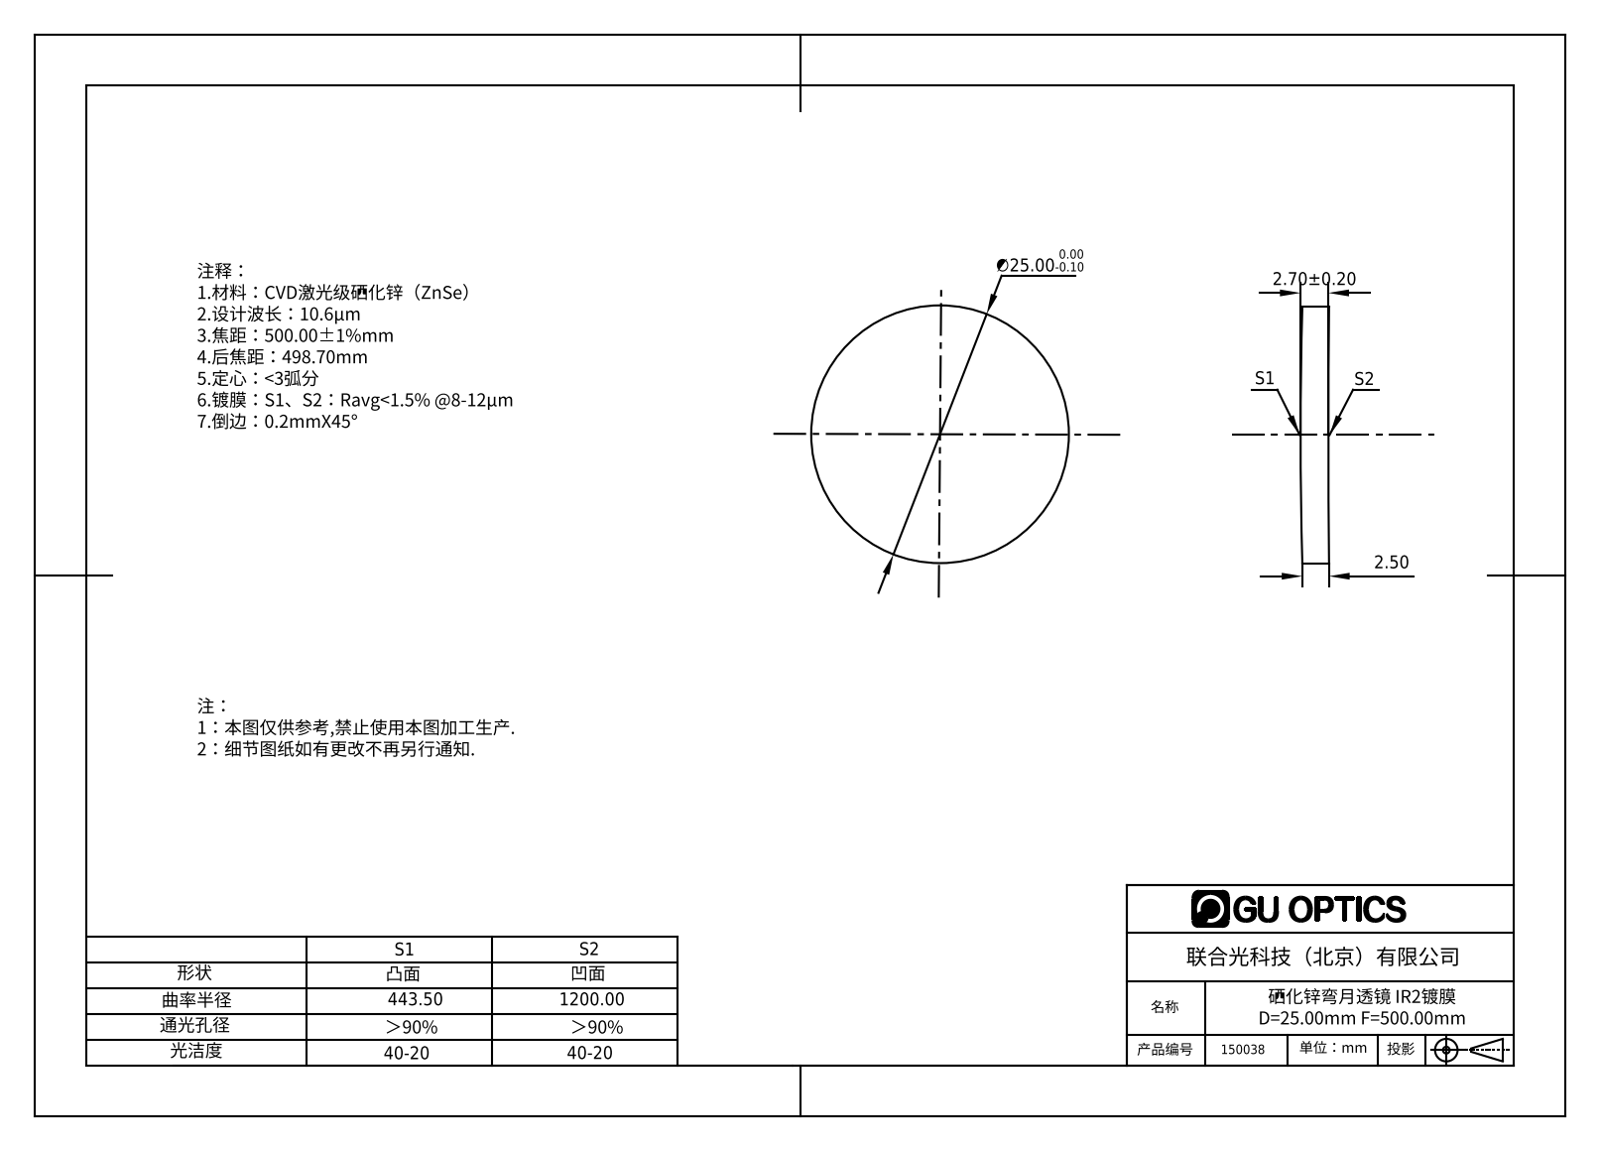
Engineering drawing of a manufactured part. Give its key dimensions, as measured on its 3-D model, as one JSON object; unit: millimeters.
{"part_name": "150013", "step_written_by": "SolidWorks 2016 (AUTOMOTIVE_DESIGN)", "units": "millimeters", "bodies": {"solids": 1, "faces": 6, "planar": 0, "cylindrical": 2, "other": 4}, "overall_size": [25, 25, 2.77], "volume_mm3": 1298, "surface_area_mm2": 1185, "round_bosses_or_shafts": [[25, 1]]}
